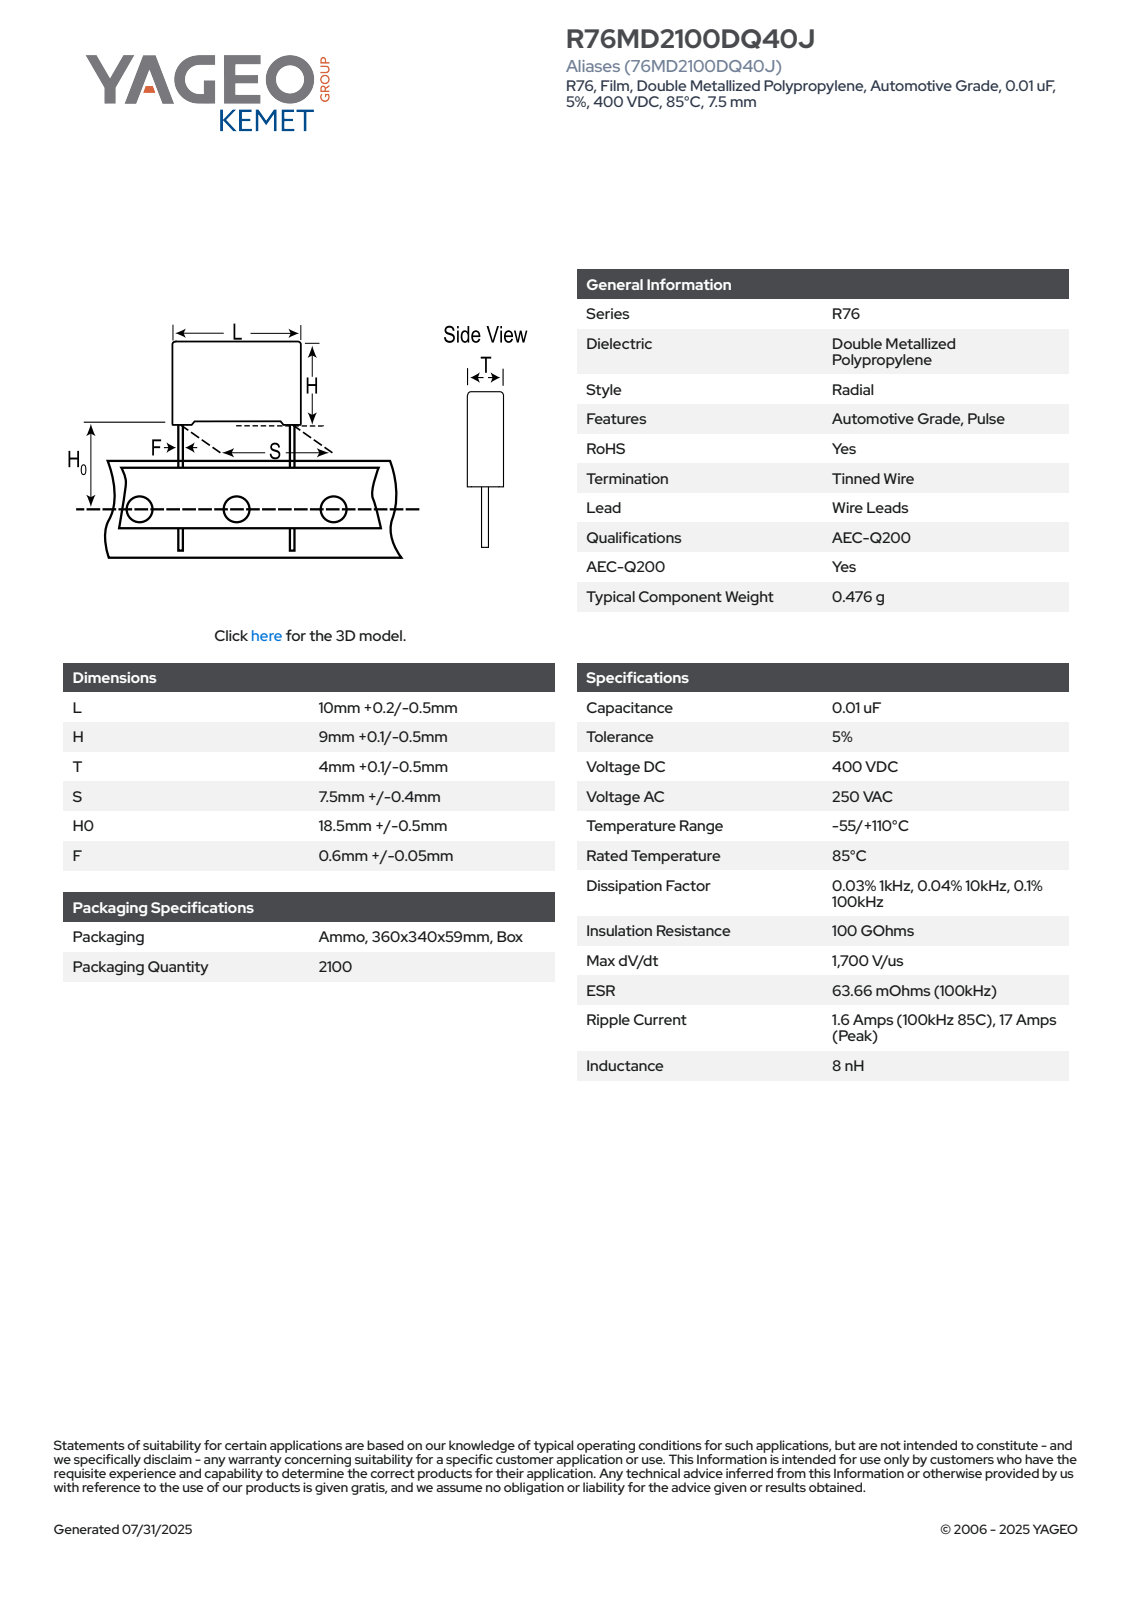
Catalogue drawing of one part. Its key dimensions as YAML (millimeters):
part_name: "CFR_RB2_10X9X4_L10.2H9.1T4.1S7.5H019F0.65"
step_written_by: "SolidWorks 2020 (AUTOMOTIVE_DESIGN)"
units: millimeters
bodies: {solids: 4, faces: 85, planar: 77, cylindrical: 8, other: 0}
overall_size: [28.1, 10.2, 4.11]
volume: 367
surface_area: 440
round_bosses_or_shafts:
  - {diameter: 0.65, count: 2}
partial_cylinders:
  - {radius: 0.5, count: 4}
face_to_face_distances: [4.1, 10.2, 8.35, 0.34, 3.76, 0.75, 9.1, 3.42, 9.86, 0.31]
